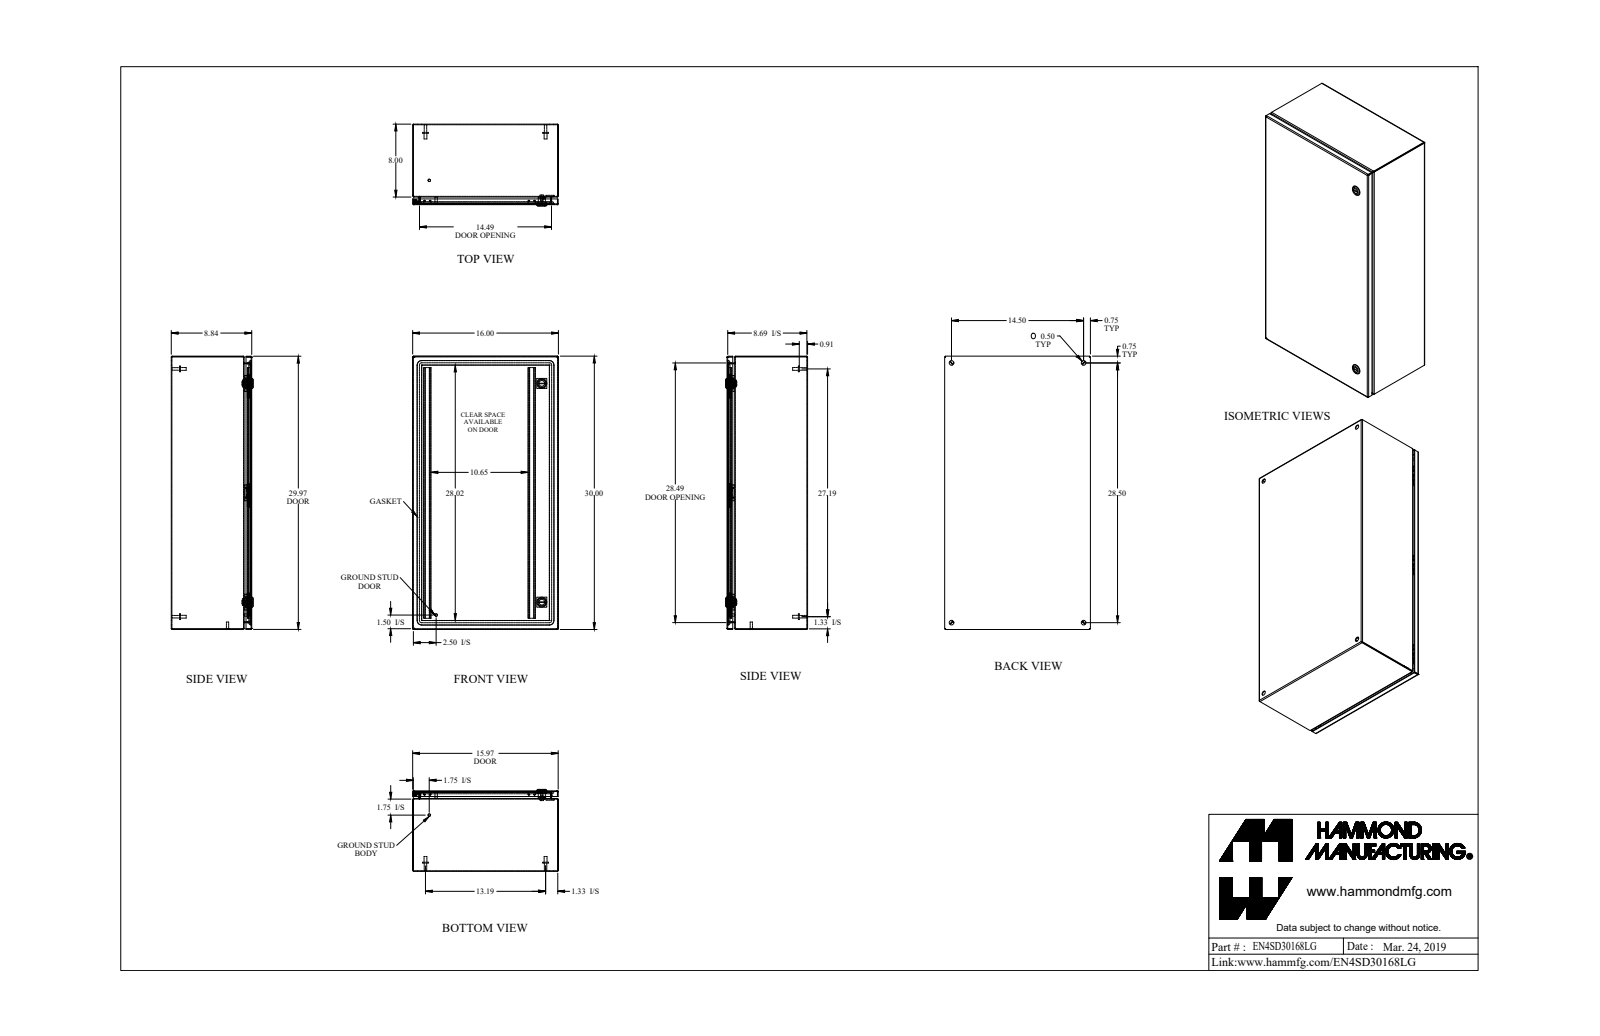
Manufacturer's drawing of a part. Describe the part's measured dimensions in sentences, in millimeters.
The part is named "EN4SD30168LG_Default". Its 3-D file was written by "SolidWorks 2019 (CONFIG_CONTROL_DESIGN)". It is 31 solids with 885 faces: 422 planar, 295 cylindrical and 168 other. Overall it measures 762 by 406.4 by 228.5 millimeters. Its volume is 2 427 000 cubic millimeters and its surface area 2 692 000 square millimeters. Round holes: 4 of diameter 12.7, 2 of diameter 5.9, 2 of diameter 15.9, 2 of diameter 19.9, 1 of diameter 4.4, 1 of diameter 6.1, 1 of diameter 6.1. Round bosses or shafts: 4 of diameter 15.9, 4 of diameter 8, 4 of diameter 6.9, 2 of diameter 27.9, 2 of diameter 13.3, 2 of diameter 7.1, 2 of diameter 6.4, 1 of diameter 11.6. Partial cylindrical surfaces (rounded edges, fillets, slot ends): 20 of radius 0.9, 20 of radius 2.7, 12 of radius 1.1, 12 of radius 2.1, 12 of radius 9.7, 8 of radius 482.7, 6 of radius 0.2, 6 of radius 1.6. The main face-to-face distances are 1.8, 222.6, 220.8, 224.5, 404.6, 760.2, 402.7, 406.4, 758.3, 762. The hole center spacings are 345.8, 368.3, 723.9, 812.2, 63.3, 63.3, 609.6, 667.3.
